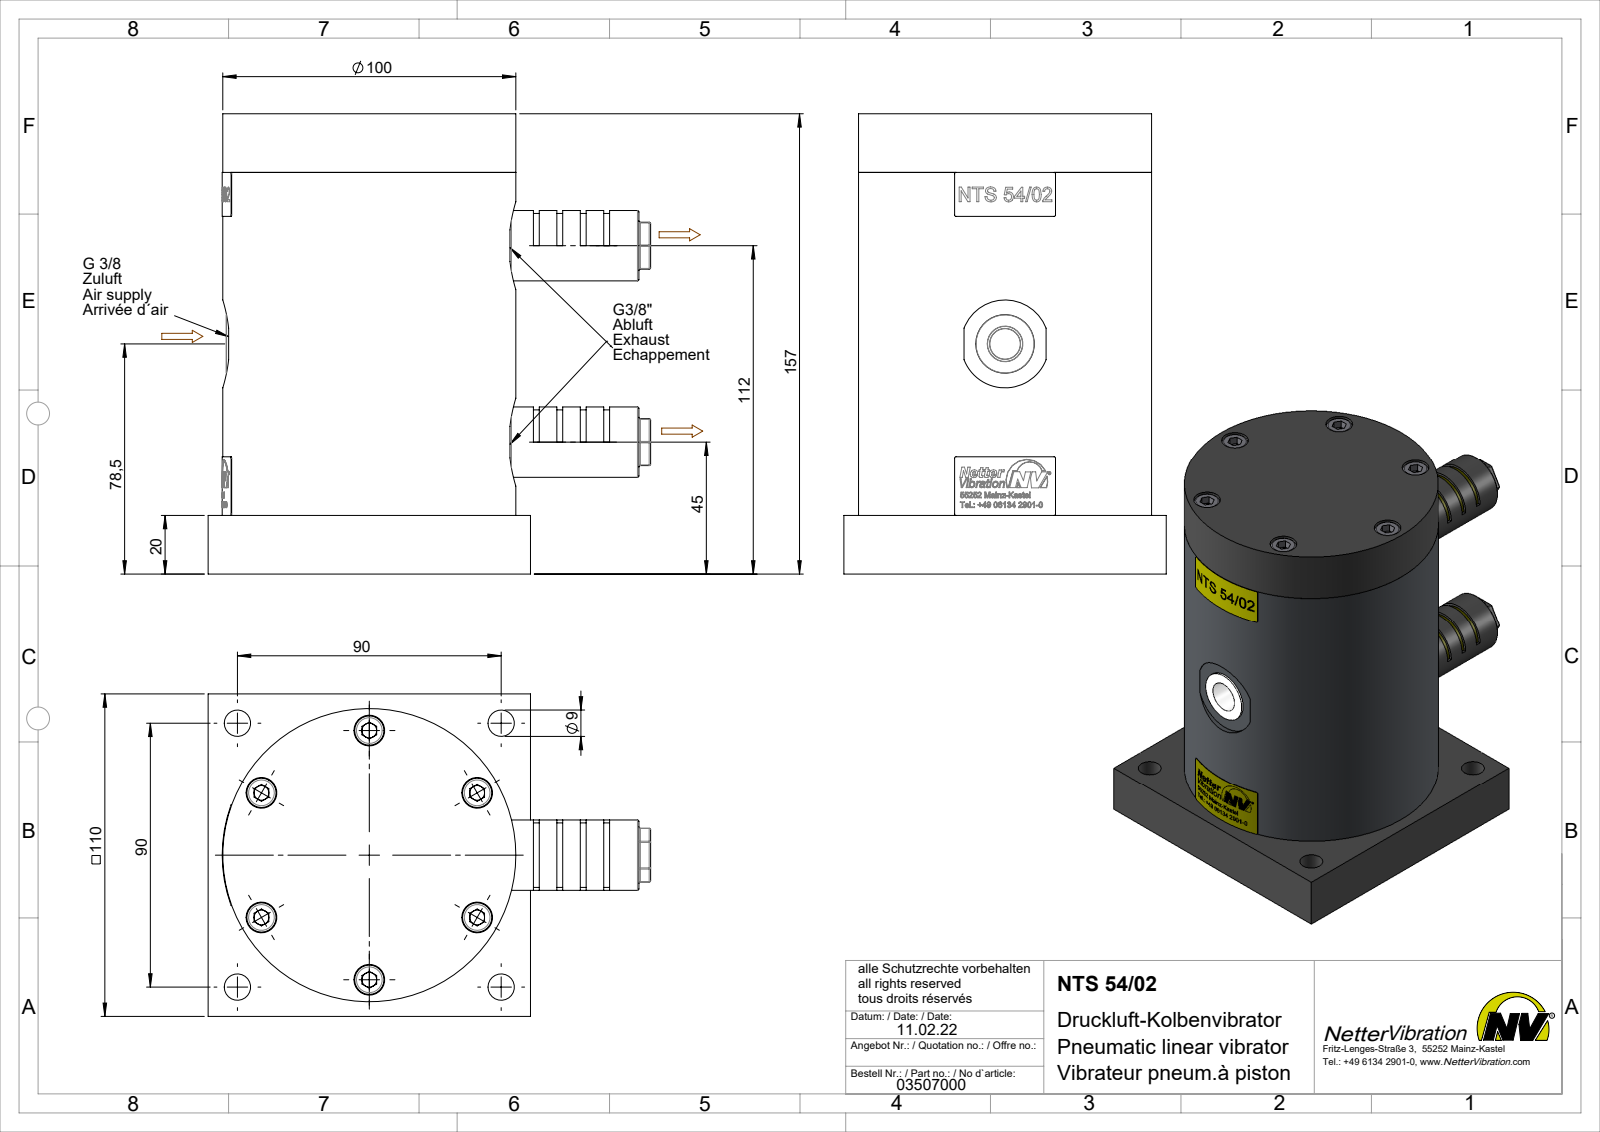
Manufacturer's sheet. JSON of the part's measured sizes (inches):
{"part_name": "NTS 54-02 Kolbenvibrator #03507000", "step_written_by": "SolidWorks 2015 (AUTOMOTIVE_DESIGN)", "units": "inches", "bodies": {"solids": 19, "faces": 762, "planar": 271, "cylindrical": 319, "other": 172}, "overall_size": [6.181, 5.945, 4.331], "volume_in3": 81.41, "surface_area_in2": 228.6, "round_holes": [[0.197, 6], [0.256, 6], [0.413, 6], [0.354, 4], [0.472, 3], [0.589, 3], [0.039, 1]], "round_bosses_or_shafts": [[0.394, 6], [0.236, 6], [0.945, 2], [0.656, 2], [3.937, 1]], "partial_cylinders_radius": [[0.02, 44], [0.591, 3], [0.433, 2], [1.976, 1]], "face_to_face_distances": [0.787, 5.394, 4.606, 6.181, 4.331, 0.276, 4.055, 0.531, 0.256, 5.925], "hole_center_spacings": [1.673, 0.989, 1.774, 2.506, 2.628, 2.898, 3.354, 3.543]}
